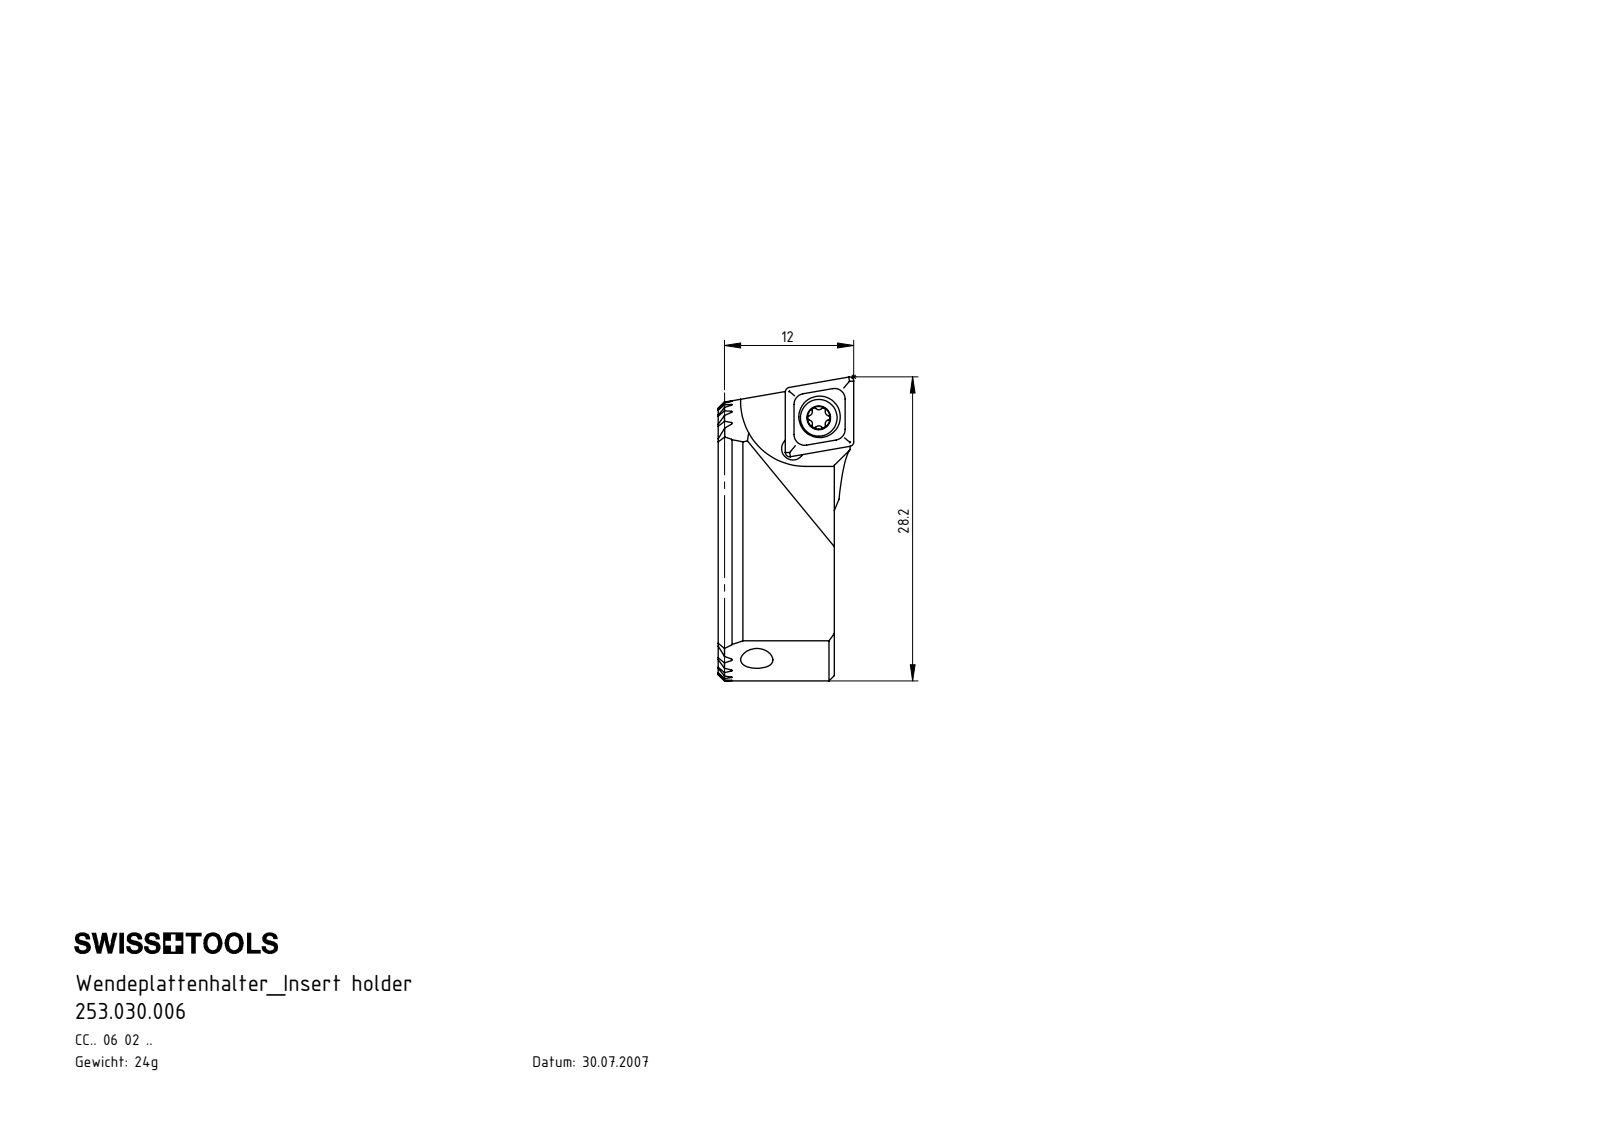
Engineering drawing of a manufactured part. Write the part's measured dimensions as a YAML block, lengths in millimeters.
part_name: "BV1.WCA.K11.012"
step_written_by: "SolidWorks 2012 (CONFIG_CONTROL_DESIGN)"
units: millimeters
bodies: {solids: 1, faces: 217, planar: 117, cylindrical: 50, other: 50}
overall_size: [27.58, 18.6, 12.24]
volume: 2789
surface_area: 2365
round_holes:
  - {diameter: 2, count: 4}
  - {diameter: 2.05, count: 1}
  - {diameter: 3, count: 1}
partial_cylinders:
  - {radius: 0.14, count: 10}
  - {radius: 2.7, count: 2}
  - {radius: 5.75, count: 2}
  - {radius: 6, count: 1}
  - {radius: 13, count: 1}
  - {radius: 13.5, count: 1}
face_to_face_distances: [1.73, 3.46, 8.66, 6.93, 10.39, 5.2, 5.19, 5, 12.12, 18.6]
hole_center_spacings: [3.89]
